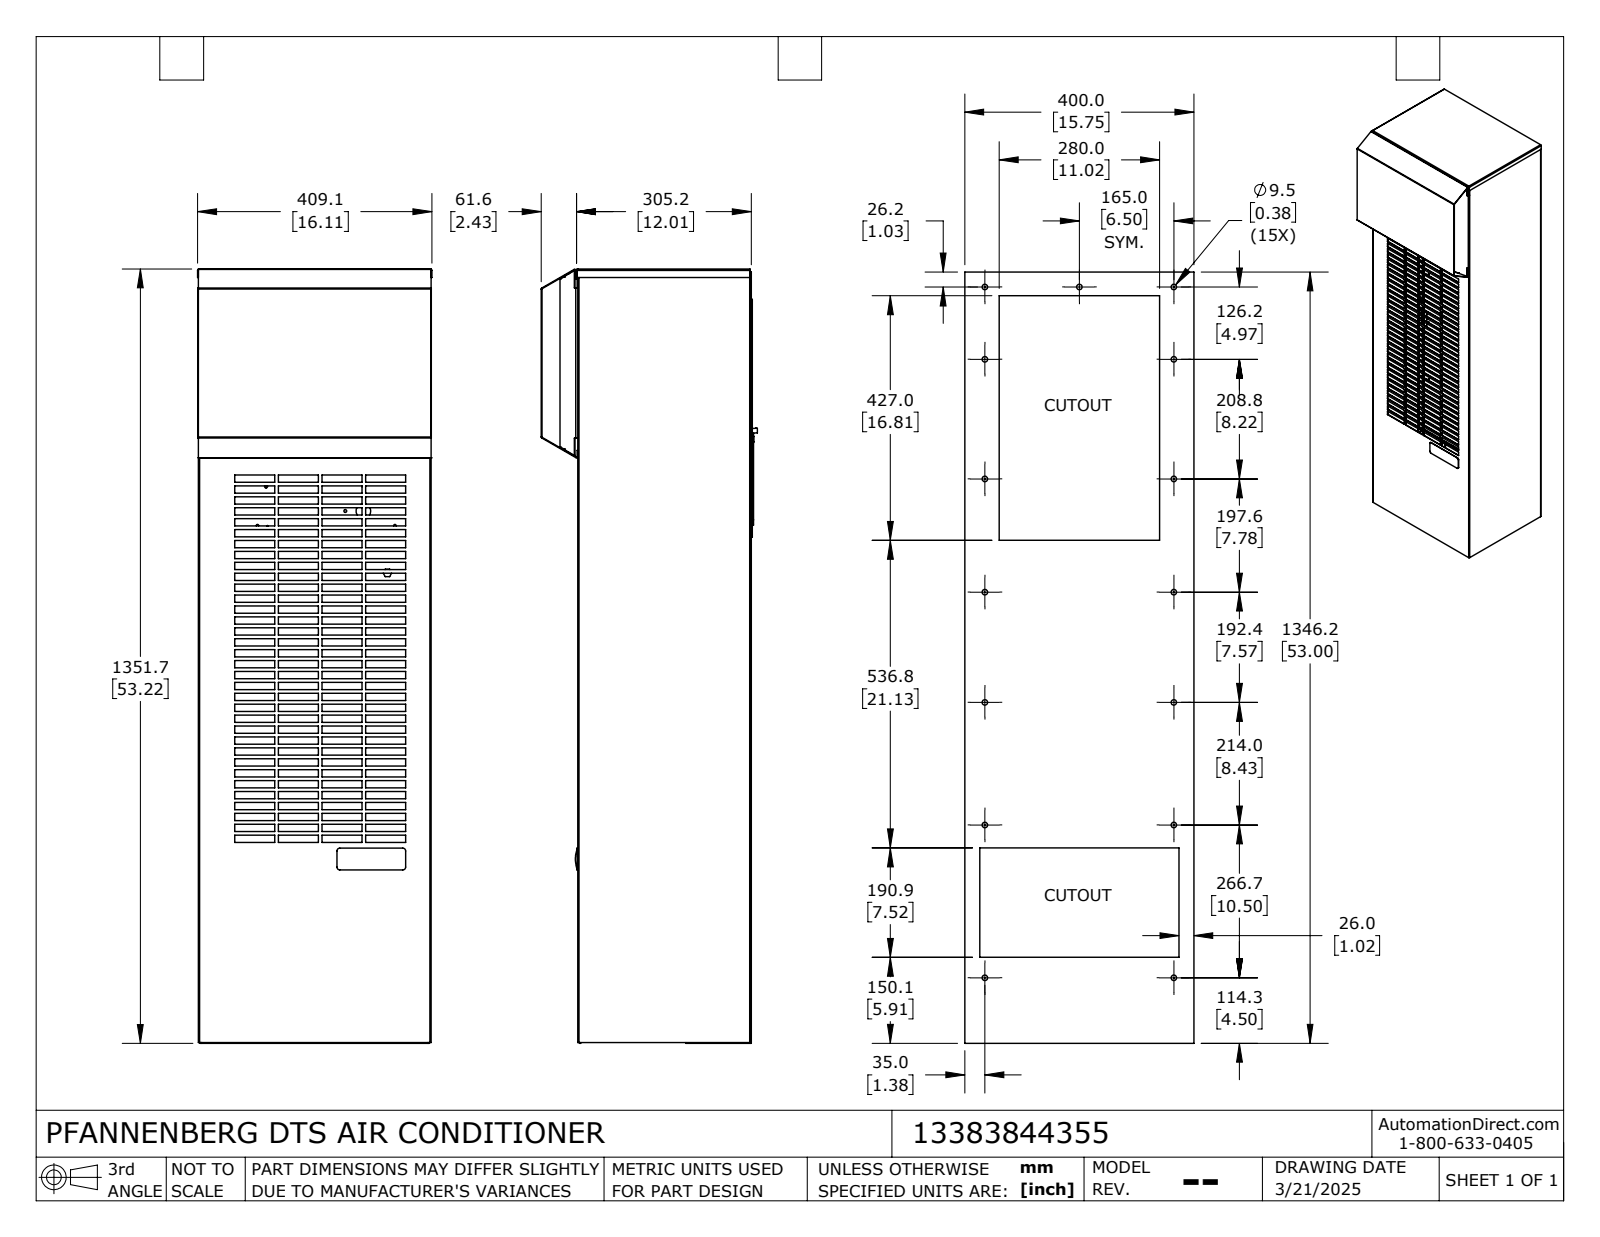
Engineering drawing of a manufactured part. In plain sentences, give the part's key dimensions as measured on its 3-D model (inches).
The part is named "13383844355_Default". Its 3-D file was written by "SolidWorks 2024 (CONFIG_CONTROL_DESIGN)". It is 25 solids with 3260 faces: 2197 planar, 955 cylindrical and 108 other. Overall it measures 53.217 by 16.106 by 14.861 inches. Its volume is 474.8 cubic inches and its surface area 11 719 square inches. Round holes: 72 of diameter 0.165, 18 of diameter 0.165, 15 of diameter 0.157, 15 of diameter 0.375, 10 of diameter 0.165, 8 of diameter 0.197, 8 of diameter 0.25, 7 of diameter 0.236, 5 of diameter 0.13, 4 of diameter 0.177, 4 of diameter 0.217, 2 of diameter 0.022. Round bosses or shafts: 5 of diameter 0.079, 2 of diameter 0.276, 2 of diameter 0.031, 1 of diameter 8.858, 1 of diameter 8.78, 1 of diameter 5.866, 1 of diameter 3.622, 1 of diameter 1.063. Partial cylindrical surfaces (rounded edges, fillets, slot ends): 140 of radius 0.125, 23 of radius 0.031, 19 of radius 0.079, 12 of radius 0.03, 12 of radius 0.078, 9 of radius 0.031, 9 of radius 0.079, 8 of radius 0.197. The main face-to-face distances are 0.048, 0.048, 15.941, 0.166, 15.99, 15.893, 4.362, 4.528, 11.923, 7.561. The hole center spacings are 0.02, 15, 4, 4.134, 1.142, 5.846, 8, 8.75.
